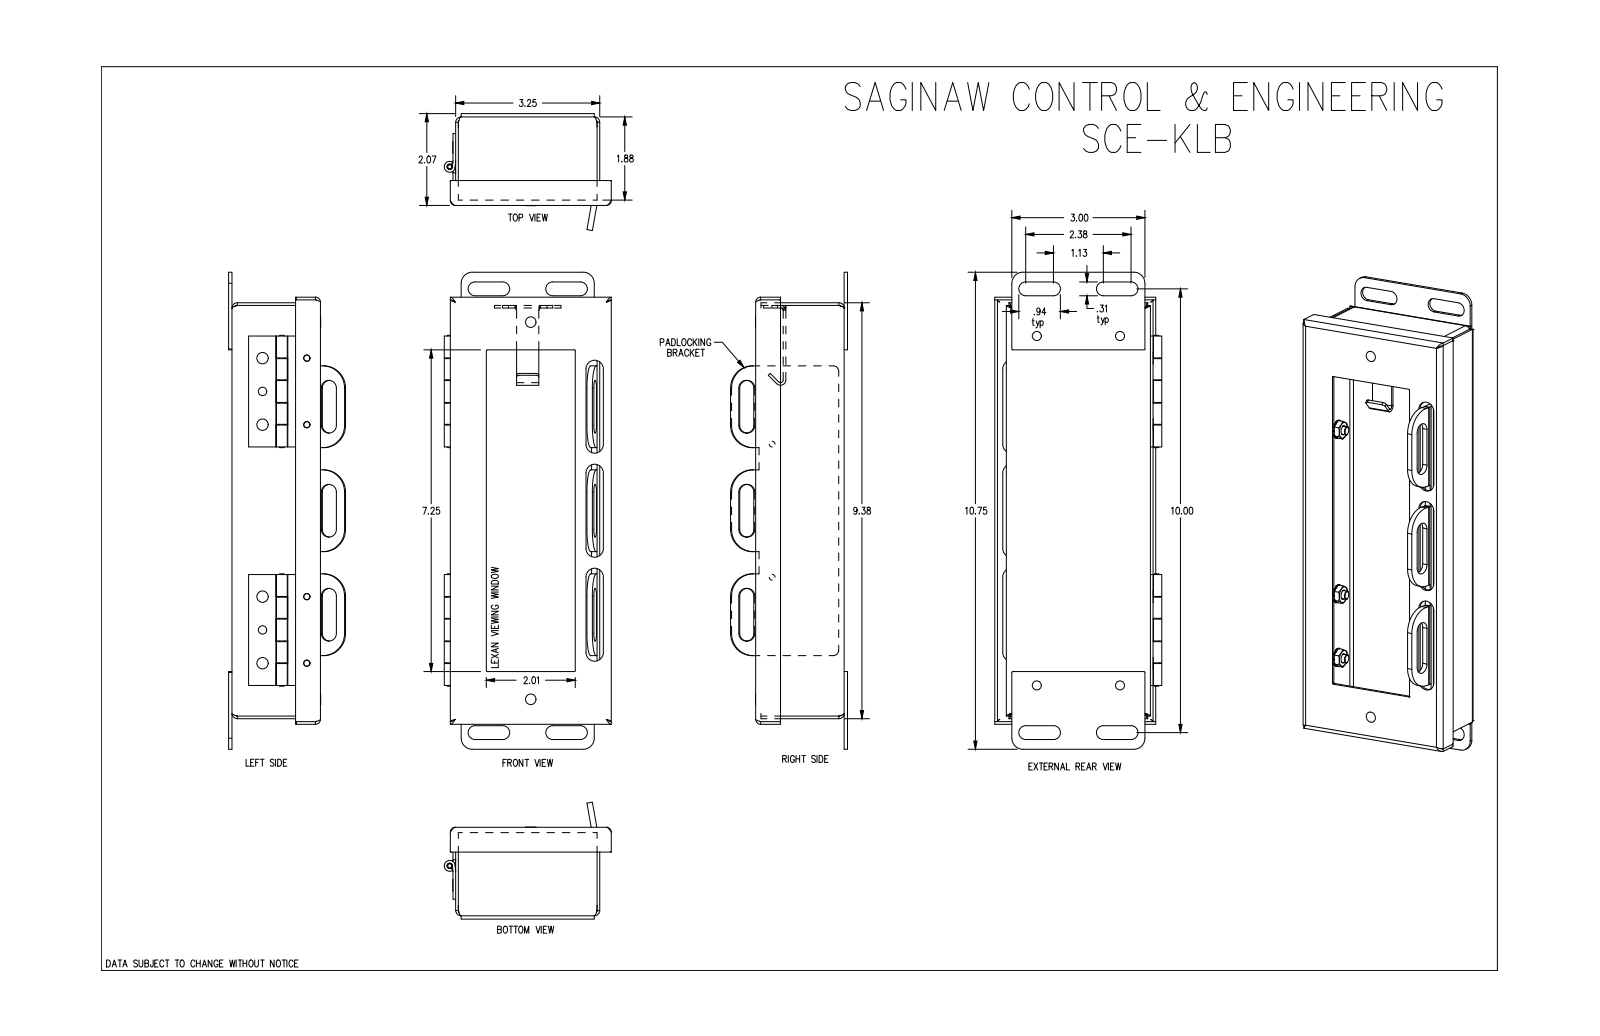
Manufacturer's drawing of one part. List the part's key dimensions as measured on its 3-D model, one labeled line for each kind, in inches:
Part name (STEP PRODUCT): SCE-KLB
STEP written by: SolidWorks 2019 (AUTOMOTIVE_DESIGN)
Units: inches
Bodies: 32 solids, 821 faces (460 planar, 257 cylindrical, 104 other)
Overall size (bounding box): 10.75 × 3.766 × 2.636
Volume: 15.82 in³ · Surface area: 370.7 in²
Round holes (diameter × count): ⌀0.19 ×6, ⌀0.13 ×4, ⌀0.136 ×4, ⌀0.193 ×4, ⌀0.203 ×4, ⌀0.17 ×2, ⌀0.188 ×2, ⌀0.125 ×1, ⌀0.25 ×1
Round bosses / shafts (diameter × count): ⌀0.256 ×4, ⌀0.188 ×4, ⌀0.237 ×2, ⌀0.162 ×2, ⌀0.111 ×2, ⌀0.245 ×1, ⌀0.12 ×1
Partial cylindrical surfaces — rounded edges, fillets, slot ends (radius × count): R0.025 ×18, R0.06 ×16, R0.12 ×16, R0.021 ×14, R0.01 ×12, R0.125 ×9, R0.25 ×9, R0.156 ×8
Main face-to-face distances: 0.06, 1.935, 3.19, 1.875, 0.125, 0.185, 3.25, 1.699, 1.639, 0.236
Hole centre spacings: 0.999, 1.802, 0.75, 1.249, 5.375, 0.924, 1.034, 1.053
